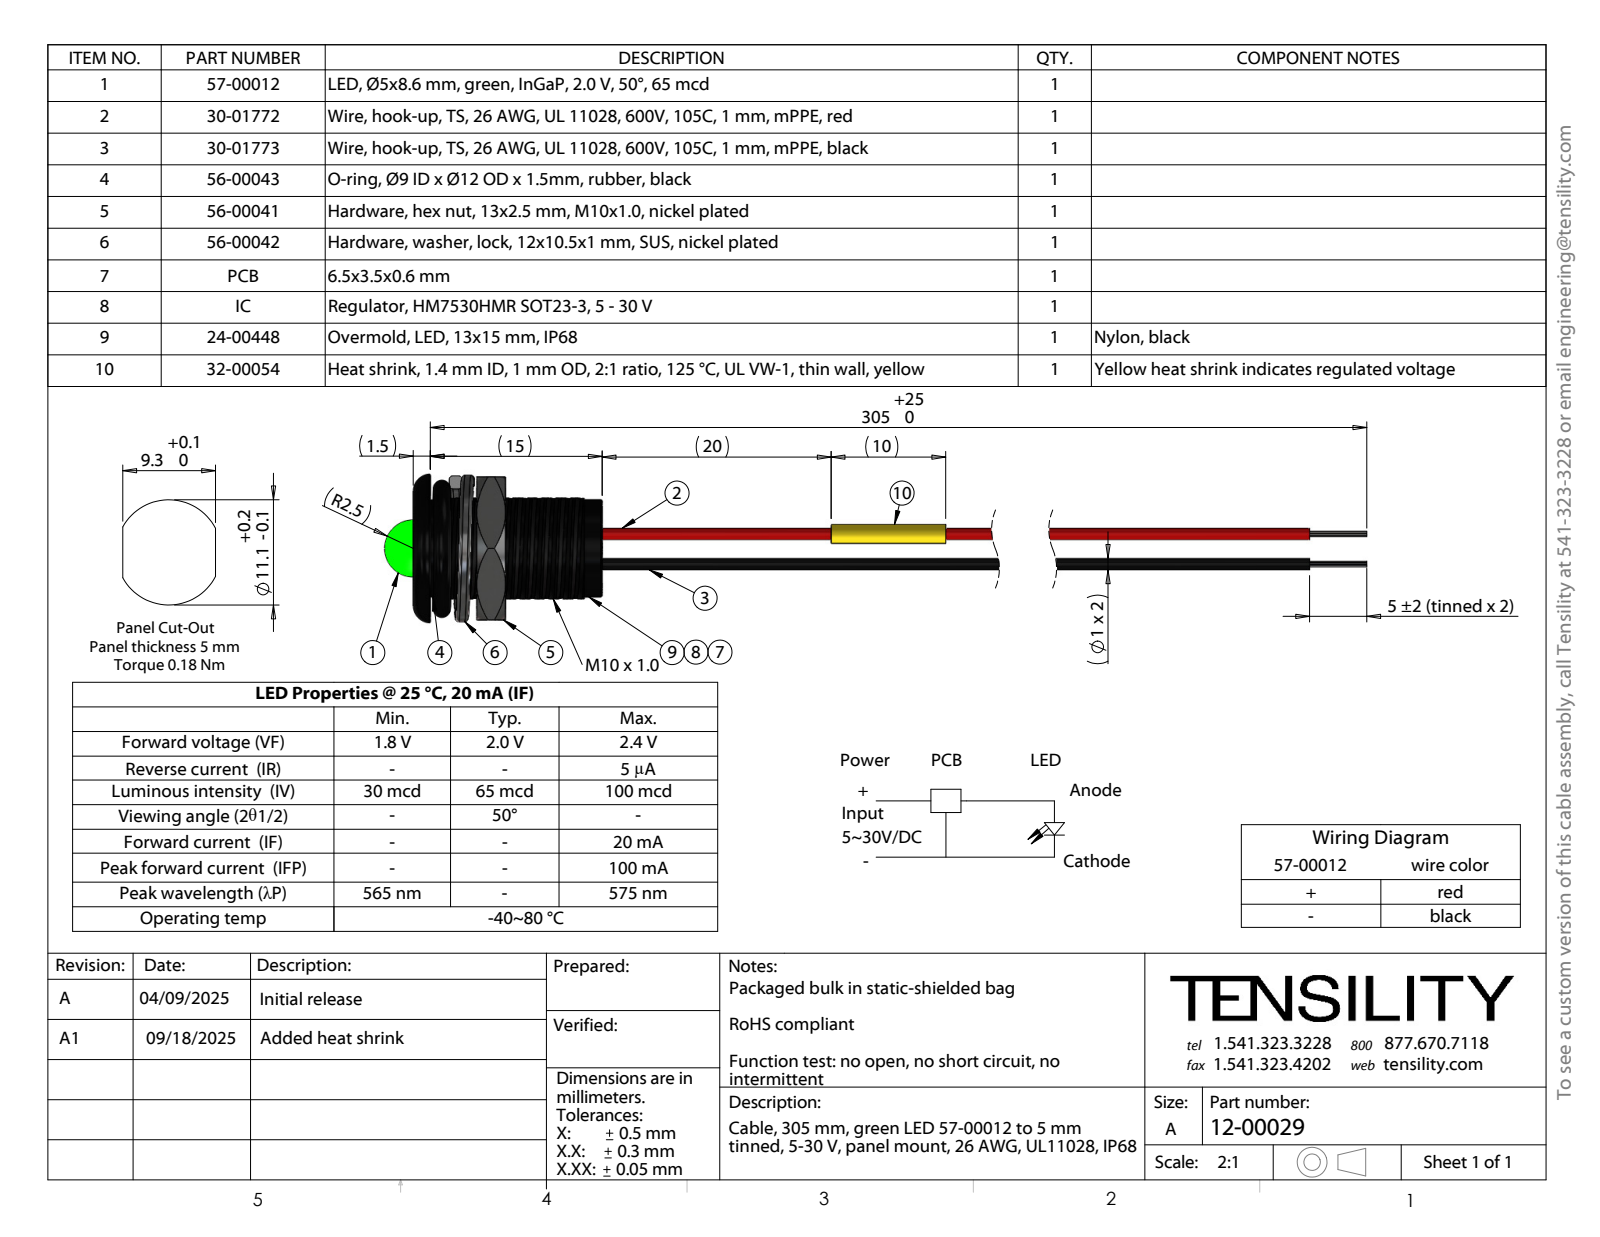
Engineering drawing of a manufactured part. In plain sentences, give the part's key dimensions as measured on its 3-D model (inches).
The part is named "30-01773_stripped and tinned; 56-00043; 12-00029_revA; 30-01772_stripped and tinned (+4 more)". Its 3-D file was written by "SolidWorks 2021 (CONFIG_CONTROL_DESIGN)". It is 57 solids with 514 faces: 185 planar, 246 cylindrical and 83 other. Overall it measures 6.85 by 0.568 by 0.511 inches. Its volume is 0.108 cubic inches and its surface area 10.18 square inches. Round holes: 2 of diameter 0.039. Round bosses or shafts: 2 of diameter 0.039, 2 of diameter 0.033, 1 of diameter 0.335, 1 of diameter 0.197. Partial cylindrical surfaces (rounded edges, fillets, slot ends): 1 of radius 0.17, 1 of radius 0.197. The main face-to-face distances are 0.059, 0.65, 0.591, 0.492, 0.317, 0.258, 0.332, 0.219, 0.16, 0.098. The hole center spacings are 0.014, 0.015, 0.013, 0.096, 0.093, 0.098, 0.099, 0.101.
